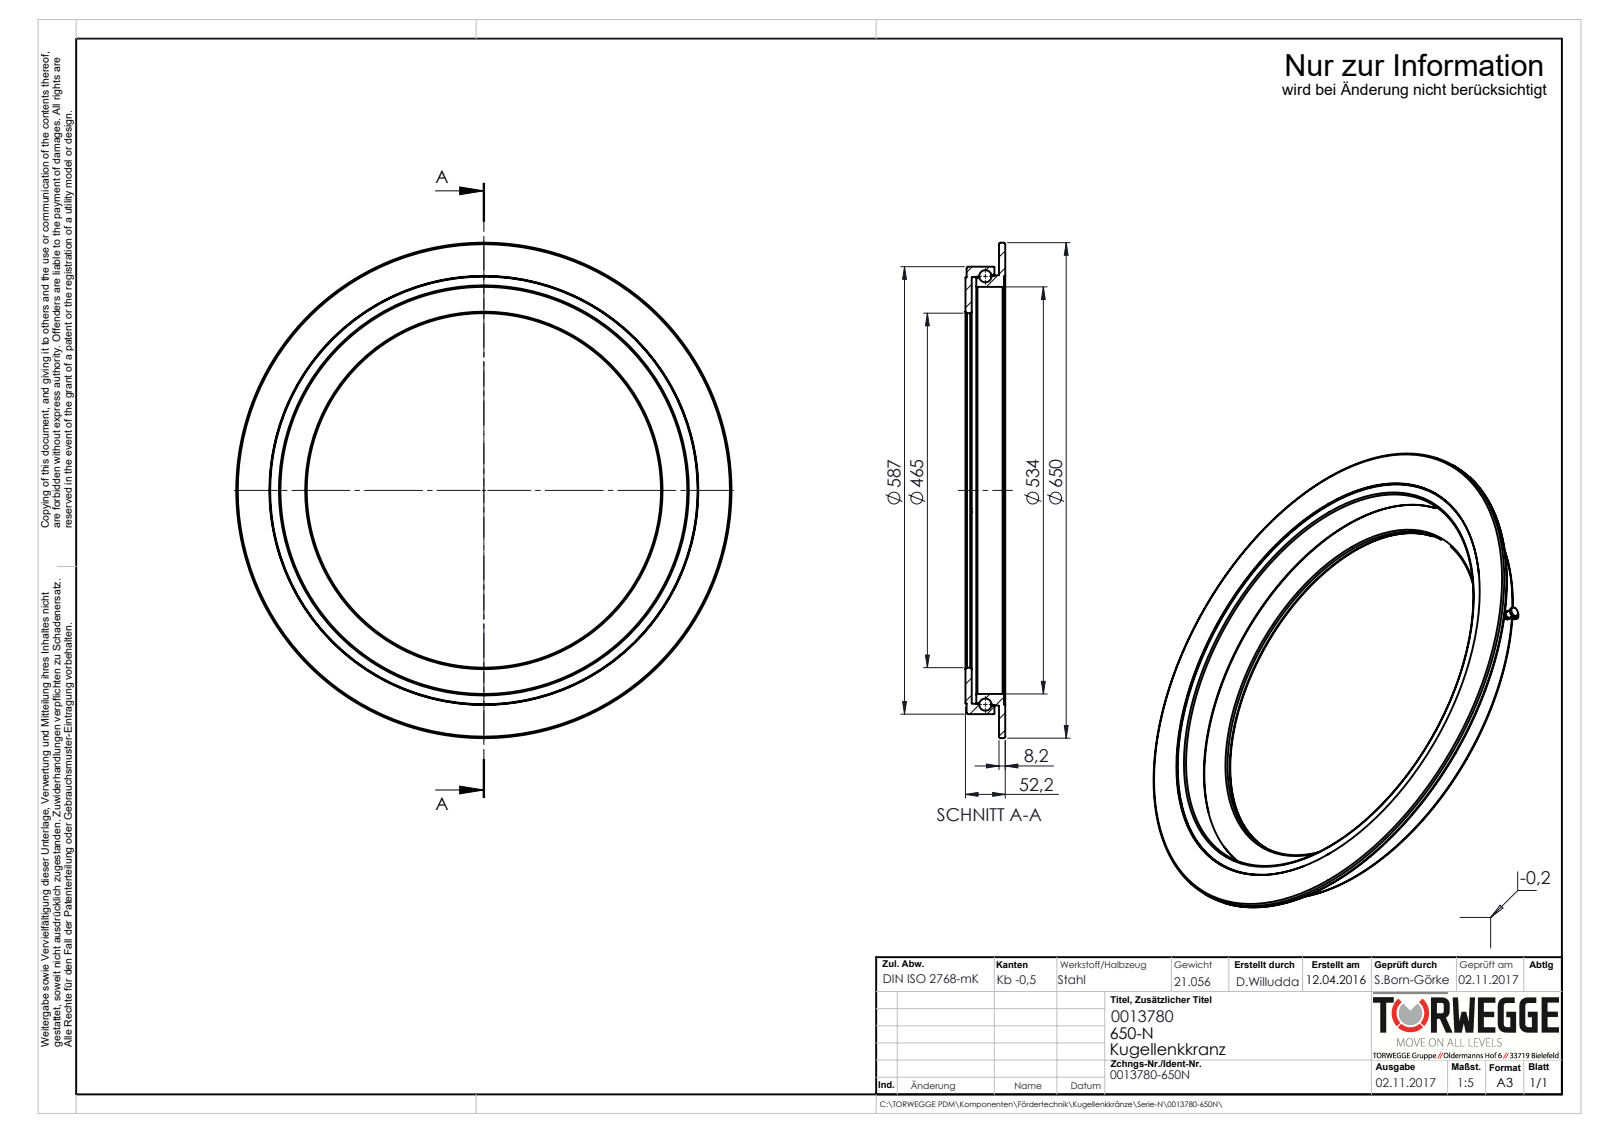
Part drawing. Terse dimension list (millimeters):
name: 0013780_650-N
written by: SolidWorks 2016 (AUTOMOTIVE_DESIGN)
unit: mm
bodies: 11 solids, 338 faces (81 planar, 109 cylindrical, 148 other)
size: 650 × 650 × 52.2
volume: 2 665 000 mm³; area: 696 948 mm²
holes: 5× ⌀1.5, 4× ⌀6, 3× ⌀4, 3× ⌀7.5, 2× ⌀4.9, 2× ⌀5.5, 1× ⌀16.5, 1× ⌀465, 1× ⌀534, 1× ⌀562
bosses: 3× ⌀12, 2× ⌀7.5, 2× ⌀4.9, 2× ⌀4.7, 1× ⌀650, 1× ⌀587, 1× ⌀559, 1× ⌀16.1
rounds: 7× R5, 3× R1.75, 3× R4.62, 3× R5.62, 1× R294.25
face distances: 8.2, 44, 35.8, 52.2, 1.5, 50.7, 6.7, 42.5, 14.2, 38
